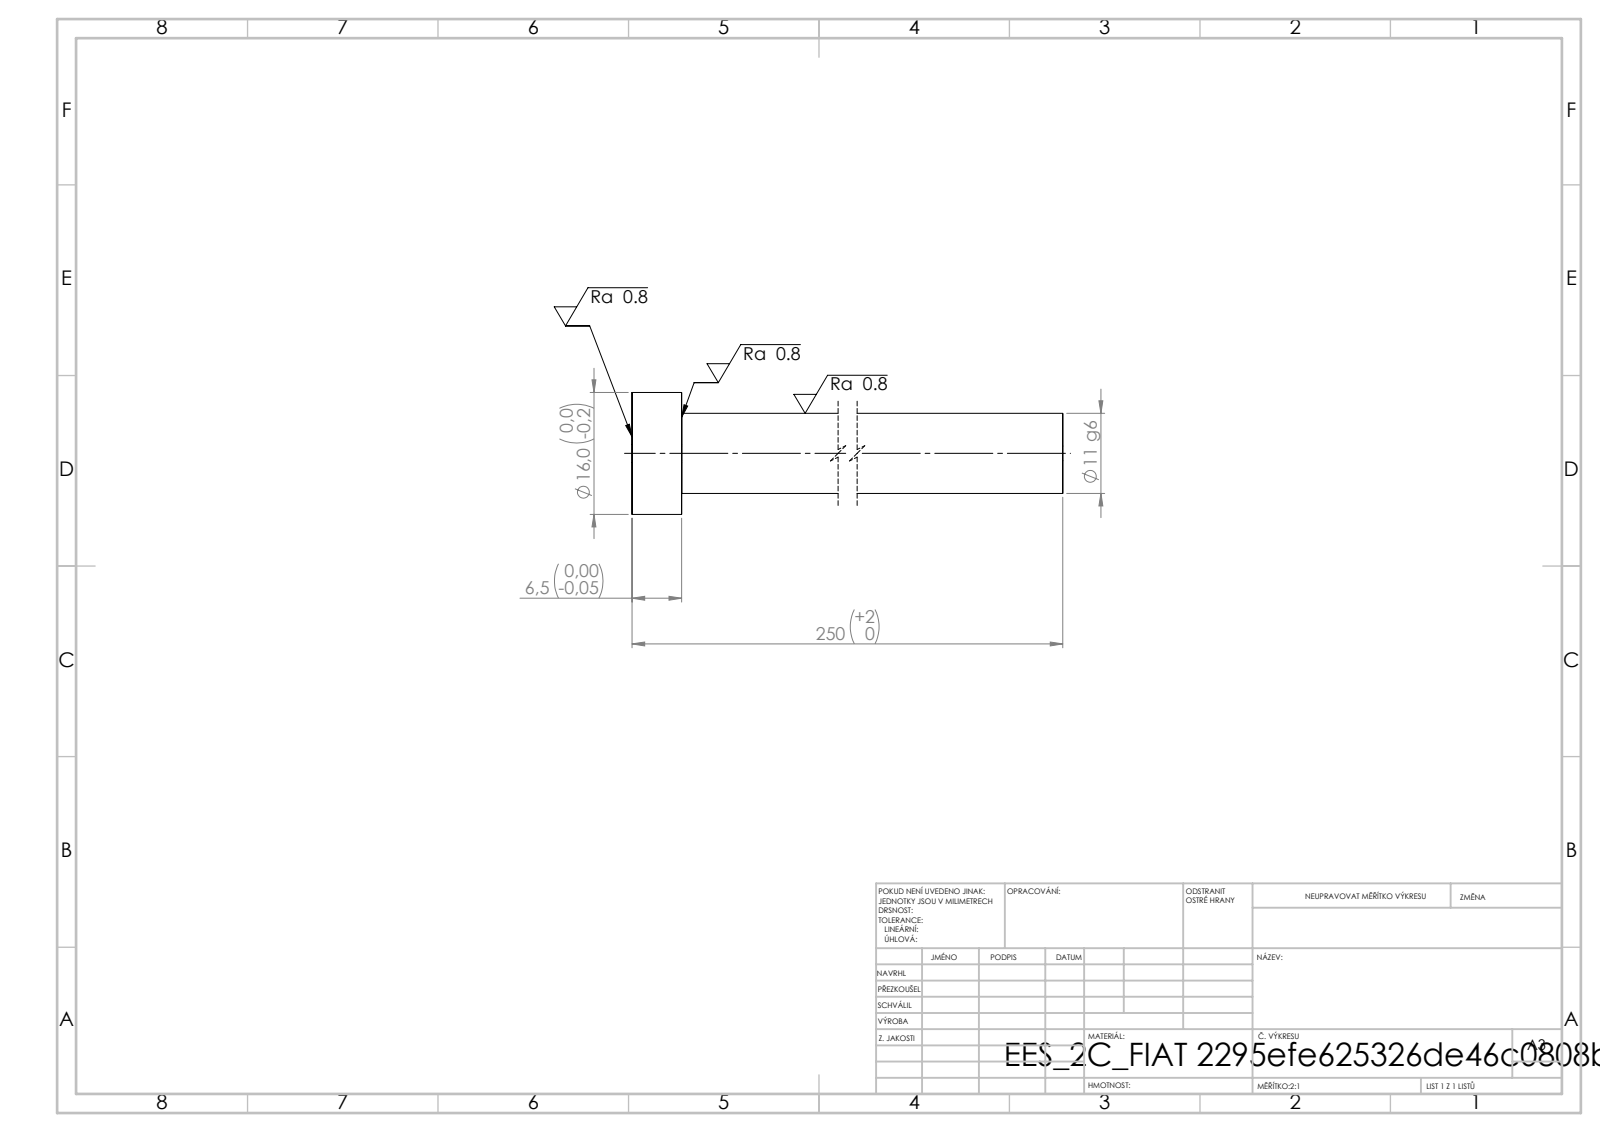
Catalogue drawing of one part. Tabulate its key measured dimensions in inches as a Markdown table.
| quantity | value |
| --- | --- |
| STEP written by | SolidWorks 2019 (CONFIG_CONTROL_DESIGN) |
| units | inches |
| bodies | 1 solid, 7 faces (3 planar, 4 cylindrical, 0 other) |
| overall size | 9.843 × 0.63 × 0.63 |
| volume | 1.366 in³ |
| surface area | 13.58 in² |
| round bosses / shafts (diameter × count) | 0.63 × 1, 0.413 × 1 |
| main face-to-face distances | 0.256, 9.843, 9.587 |
